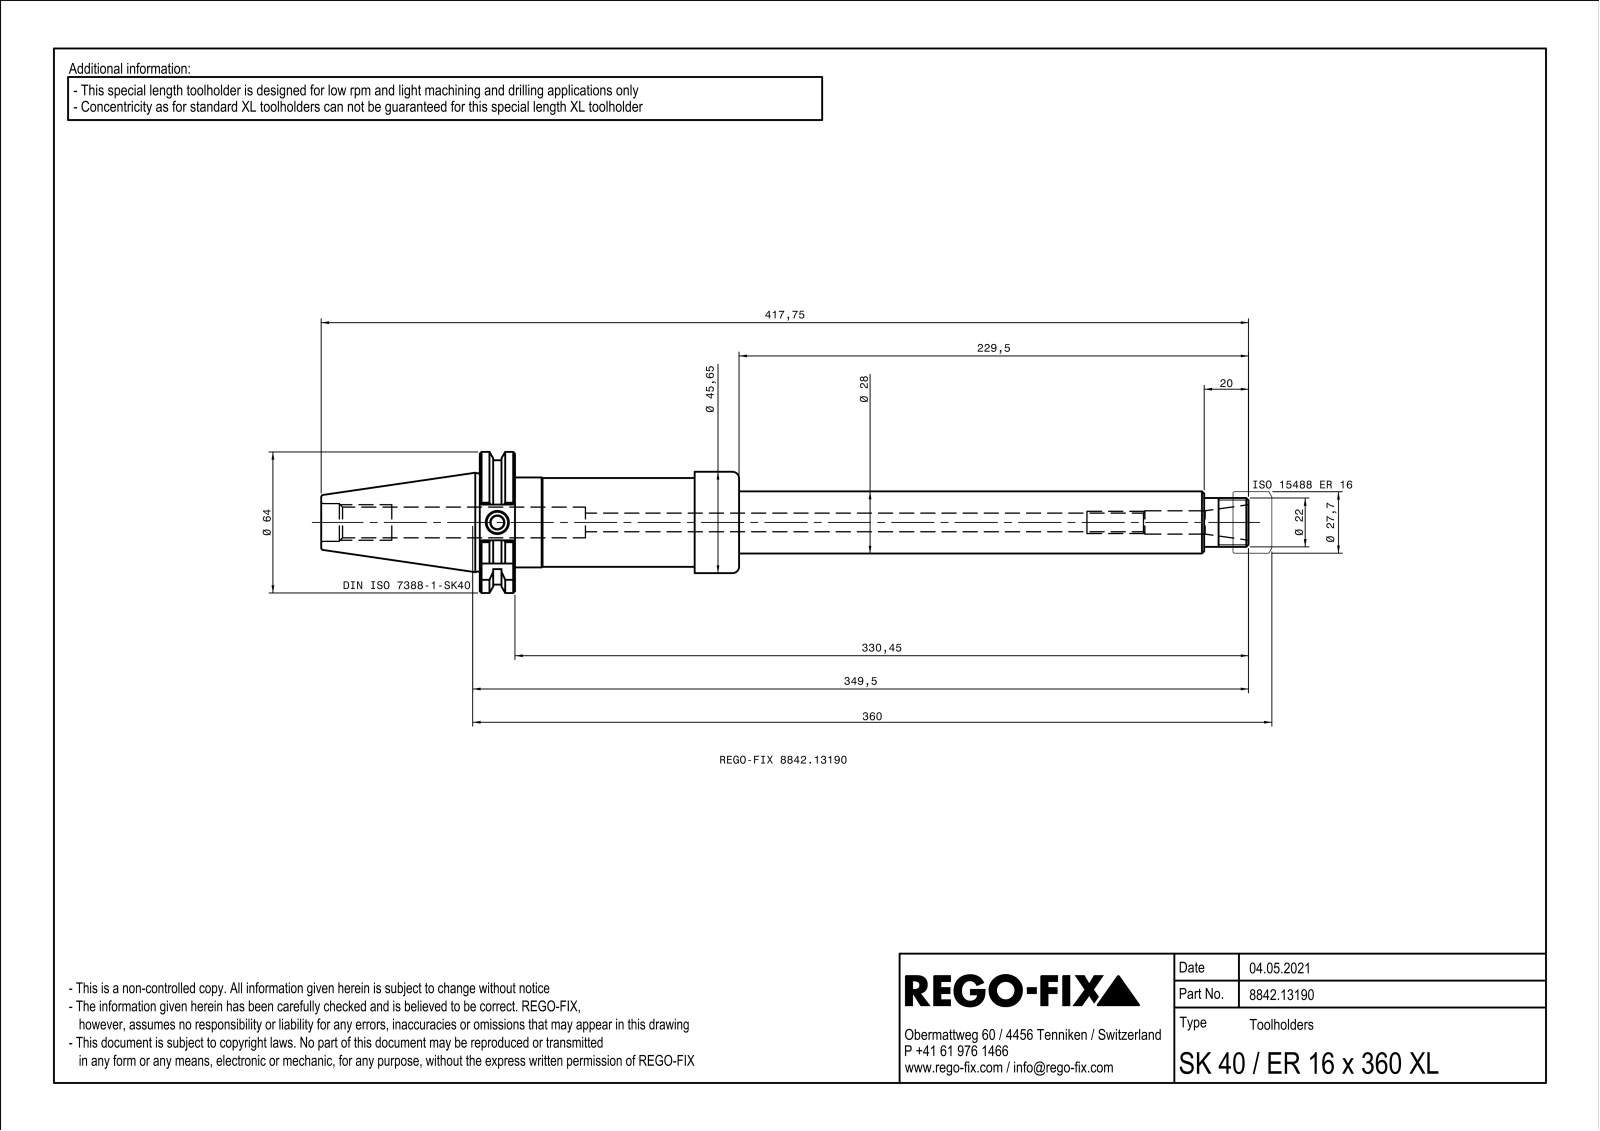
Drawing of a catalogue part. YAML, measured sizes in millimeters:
part_name: "NOCUT"
step_written_by: "SIEMENS PLM Software Solid Edge ST10 (AUTOMOTIVE_DESIGN)"
units: millimeters
bodies: {solids: 1, faces: 160, planar: 51, cylindrical: 44, other: 65}
overall_size: [417.75, 63.55, 61.01]
volume: 336353
surface_area: 71007
round_holes:
  - {diameter: 10, count: 2}
  - {diameter: 6, count: 1}
  - {diameter: 8.35, count: 1}
  - {diameter: 8.38, count: 1}
  - {diameter: 10.5, count: 1}
  - {diameter: 13.84, count: 1}
  - {diameter: 17, count: 1}
  - {diameter: 25, count: 1}
  - {diameter: 29, count: 1}
  - {diameter: 38.38, count: 1}
  - {diameter: 40.05, count: 1}
  - {diameter: 43.3, count: 1}
round_bosses_or_shafts:
  - {diameter: 45.65, count: 1}
  - {diameter: 40.5, count: 1}
  - {diameter: 40, count: 1}
  - {diameter: 34, count: 1}
  - {diameter: 33, count: 1}
  - {diameter: 28, count: 1}
  - {diameter: 24.7, count: 1}
  - {diameter: 23.8, count: 1}
partial_cylinders:
  - {radius: 0.5, count: 13}
  - {radius: 28, count: 1}
  - {radius: 31.77, count: 1}
face_to_face_distances: [15.85, 100.95, 116.8, 6, 14, 20, 1.5, 99.45, 115.3, 18.5]
